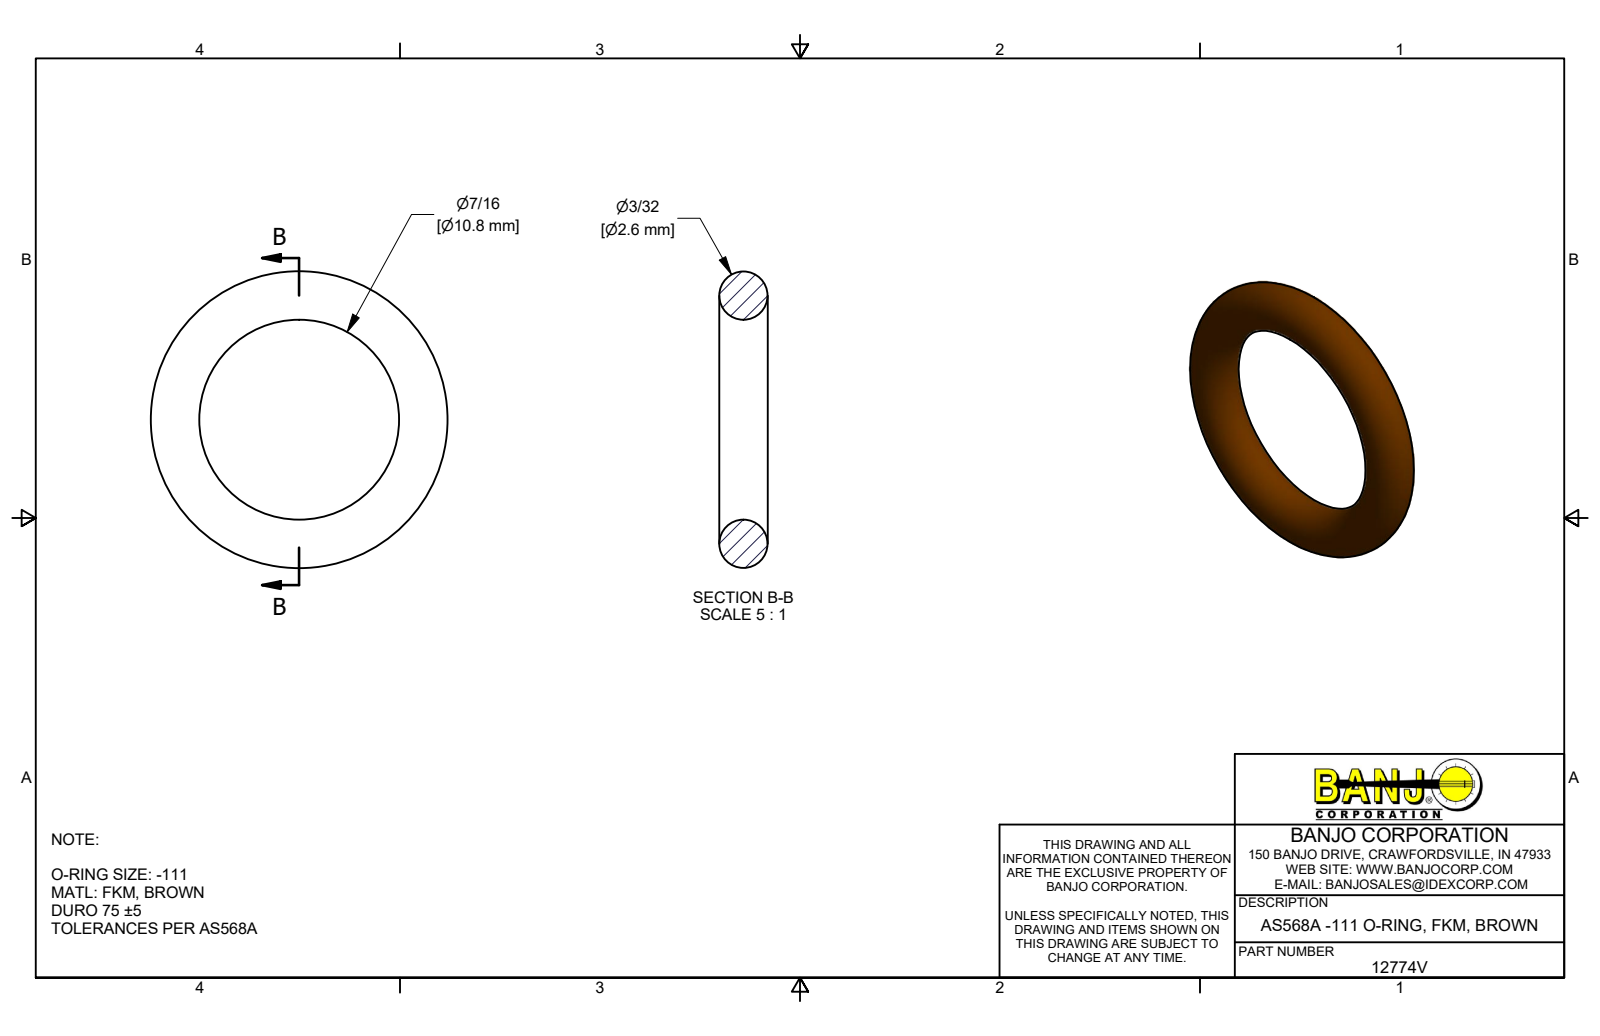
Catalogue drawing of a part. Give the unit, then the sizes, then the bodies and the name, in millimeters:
Units: millimetres
Overall size (bounding box): 16 × 16 × 2.6
Volume: 230 mm³ · Surface area: 346 mm²
Bodies: 1 solid, 1 faces (0 planar, 0 cylindrical, 1 other)
Part name (STEP PRODUCT): 12774V
STEP written by: Autodesk Inventor 2019 (AUTOMOTIVE_DESIGN)
